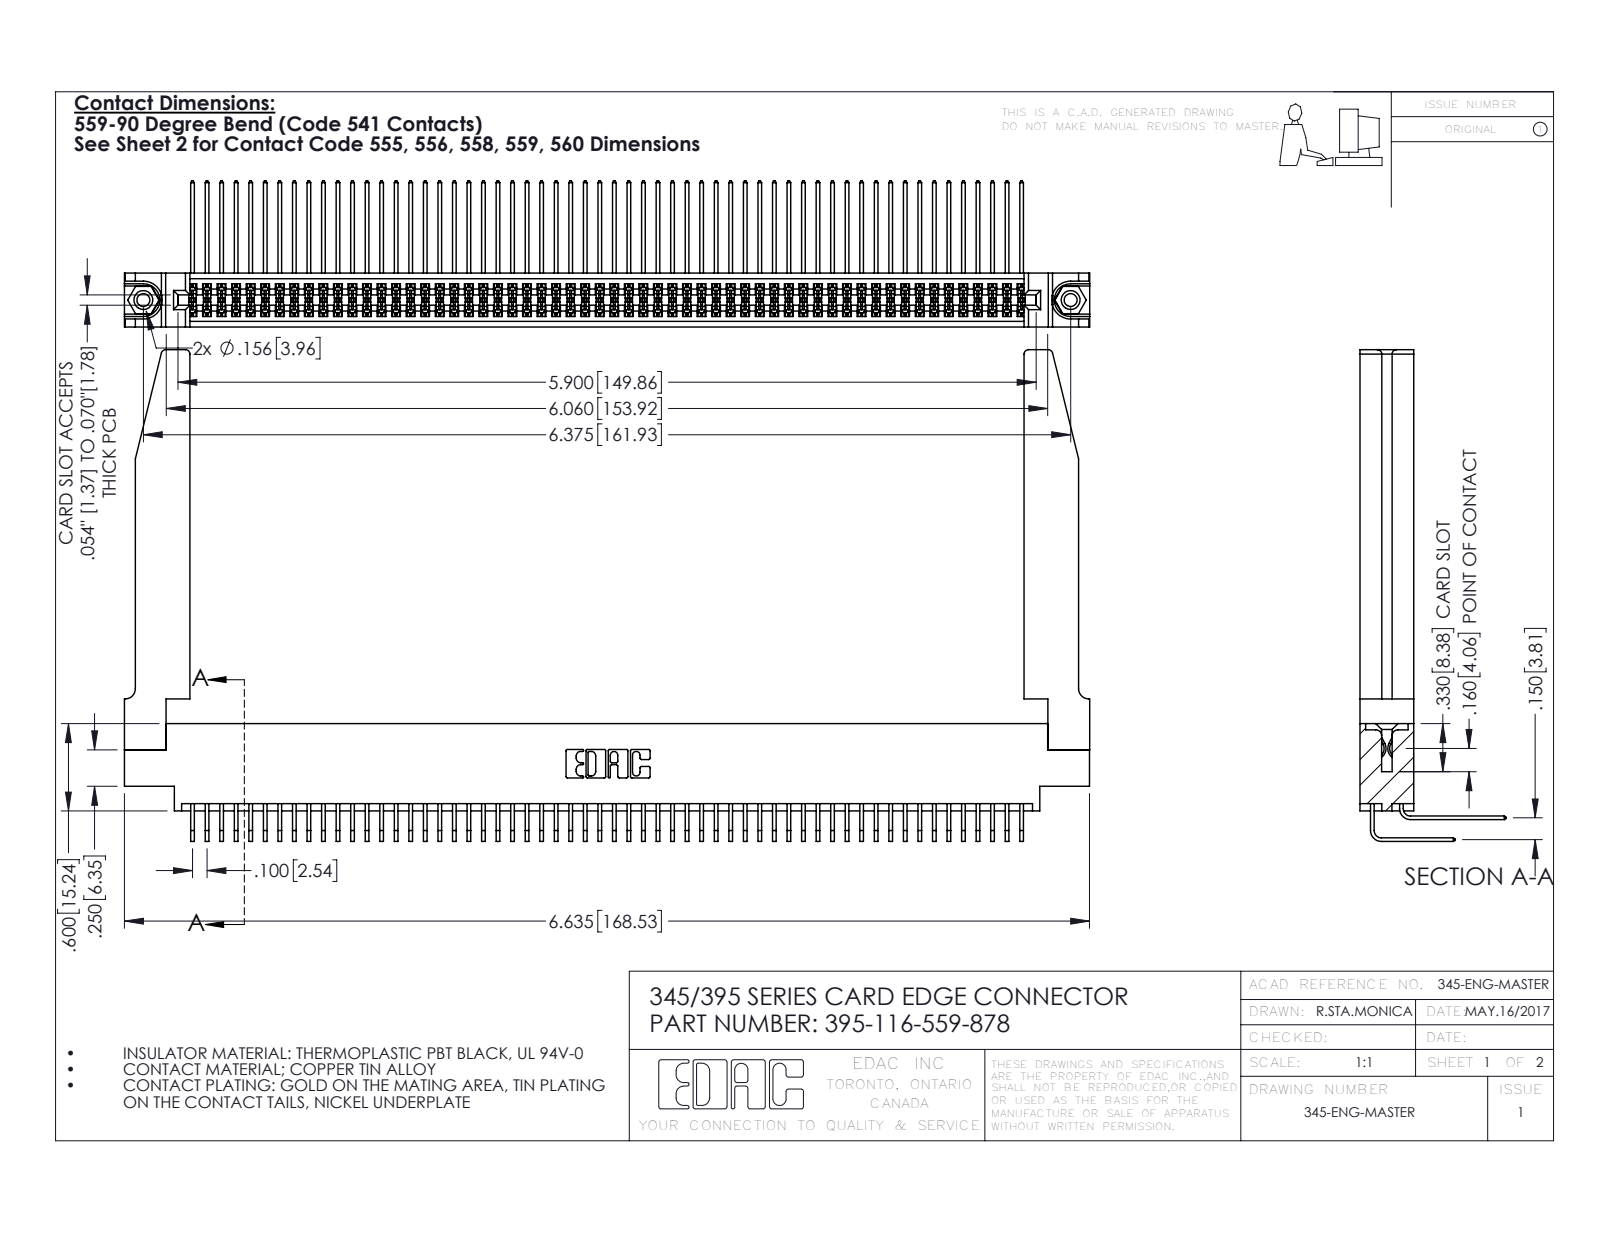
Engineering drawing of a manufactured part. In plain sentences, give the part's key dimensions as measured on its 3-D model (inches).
The part is named "345-292-001_559 Tail - 2; 345-292-001_558 559 Tail - 1; 345-220-078_345-220-078; 395-116-559-878 (+2 more)". Its 3-D file was written by "SolidWorks 2016 (CONFIG_CONTROL_DESIGN)". It is 121 solids with 6396 faces: 4286 planar, 2058 cylindrical and 52 other. Overall it measures 6.636 by 3.379 by 1.005 inches. Its volume is 1.516 cubic inches and its surface area 55.31 square inches. Round holes: 2 of diameter 0.089, 2 of diameter 0.125, 2 of diameter 0.156, 1 of diameter 0.064. Round bosses or shafts: 2 of diameter 0.155. Partial cylindrical surfaces (rounded edges, fillets, slot ends): 175 of radius 0.006, 22 of radius 0.01, 8 of radius 0.03, 6 of radius 0.007, 6 of radius 0.031, 3 of radius 0.026, 2 of radius 0.014, 2 of radius 0.019. The main face-to-face distances are 0.072, 0.37, 0.298, 0.098, 0.272, 0.025, 0.2, 0.225, 0.15, 0.175. The hole center spacings are 0.27, 6.139, 6.375.
